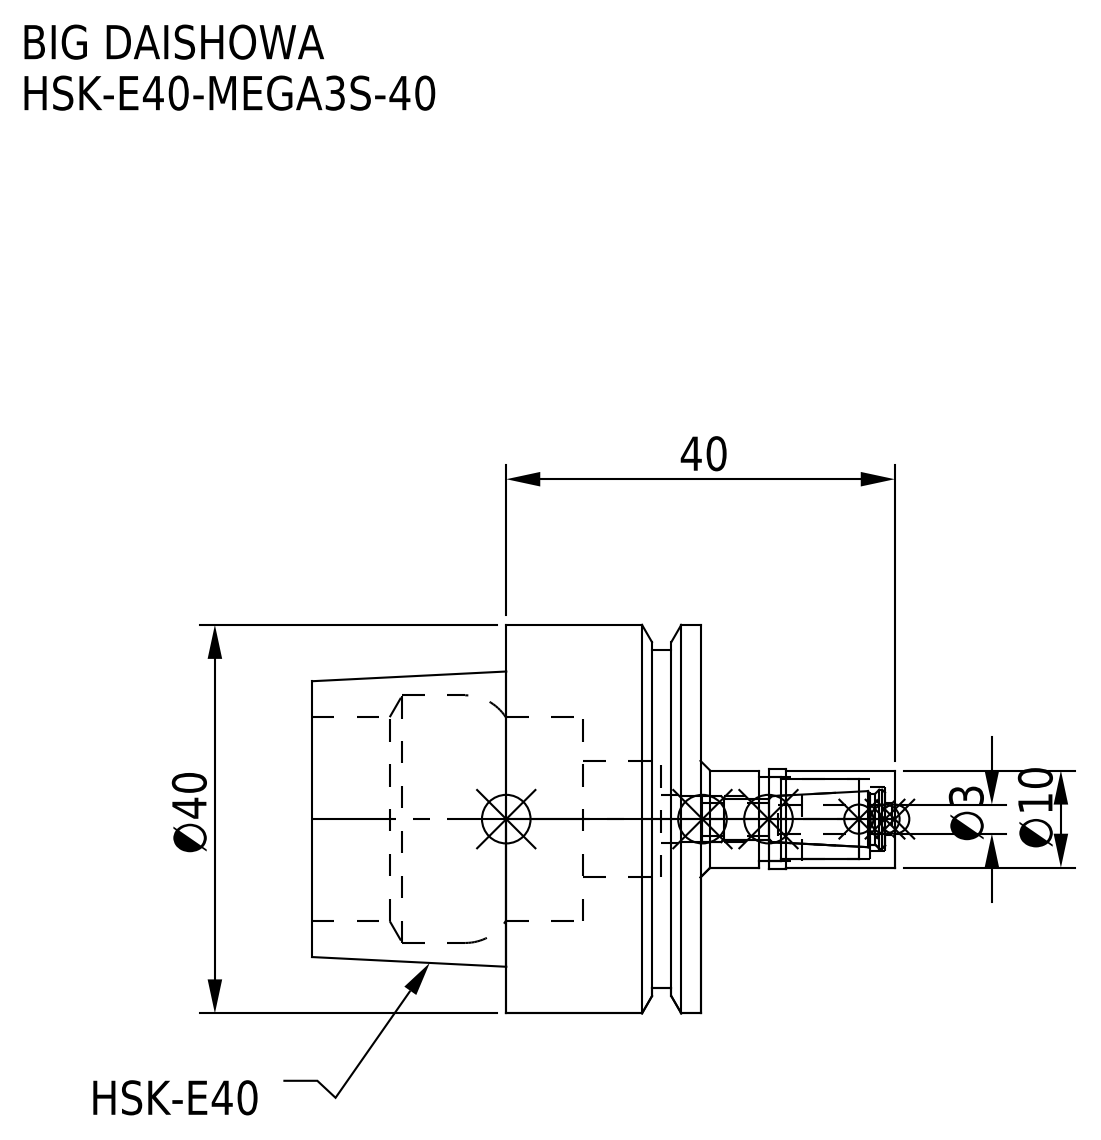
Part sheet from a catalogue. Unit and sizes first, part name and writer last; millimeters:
Units: millimetres
Overall size (bounding box): 60 × 40 × 40
Round holes (diameter × count): ⌀3.3 ×1, ⌀4.7 ×1, ⌀4.9 ×1, ⌀5 ×1, ⌀6.6 ×1, ⌀8.2 ×1, ⌀8.7 ×1, ⌀12 ×1, ⌀21 ×1, ⌀25.5 ×1
Round bosses / shafts (diameter × count): ⌀40 ×1, ⌀34.8 ×1, ⌀10.3 ×1, ⌀10 ×1
Main face-to-face distances: 20, 40, 12.05, 7.95, 27.95, 8, 4.05, 15.95, 35.95, 5
Volume: 26 705 mm³ · Surface area: 11 198 mm²
Bodies: 2 solids, 74 faces (18 planar, 40 cylindrical, 16 other)
Part name (STEP PRODUCT): HSK-E40-MEGA3S-40-030.stp; HSK-E40-MEGA3S-40_1.stp; HSK-E40-MEGA3S-40; HE40MS03040-030_ASM.stp (+3 more)
STEP written by: SolidWorks 2019 (CONFIG_CONTROL_DESIGN)
